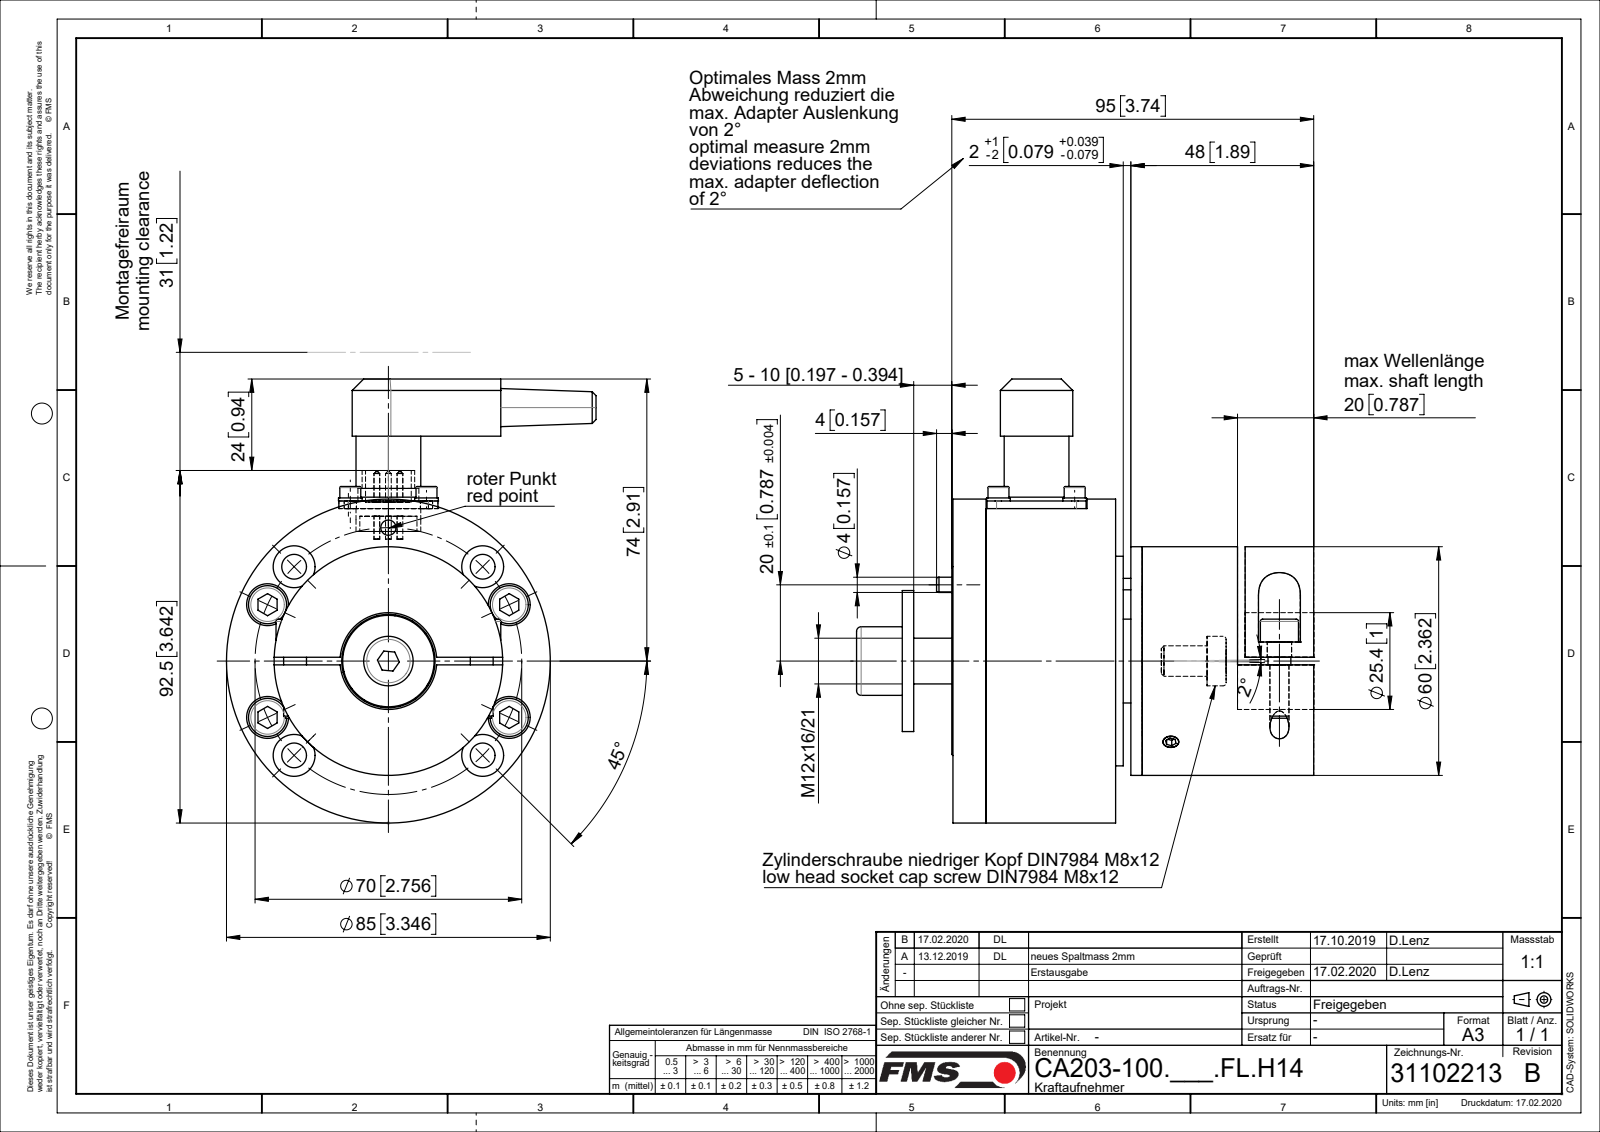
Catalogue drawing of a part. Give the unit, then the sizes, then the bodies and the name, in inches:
Units: inches
Overall size (bounding box): 4.744 × 4.587 × 3.819
Round holes (diameter × count): ⌀0.102 ×8, ⌀0.256 ×8, ⌀0.433 ×8, ⌀0.203 ×6, ⌀0.079 ×5, ⌀0.126 ×4, ⌀0.142 ×4, ⌀0.157 ×4, ⌀0.276 ×4, ⌀0.252 ×2, ⌀0.118 ×1, ⌀0.17 ×1
Round bosses / shafts (diameter × count): ⌀0.236 ×10, ⌀0.118 ×8, ⌀0.394 ×6, ⌀0.059 ×5, ⌀0.244 ×4, ⌀0.217 ×4, ⌀0.197 ×4, ⌀3.346 ×1
Partial cylindrical surfaces — rounded edges, fillets, slot ends (radius × count): R0.098 ×4, R0.197 ×2, R0.217 ×2, R0.374 ×1
Main face-to-face distances: 1.772, 1.949, 0.354, 0.079, 0.453, 1.24, 0.394, 1.693, 0.059, 1.594
Hole centre spacings: 0.787, 0.976, 0.992, 1.291, 1.378, 2.013, 2.223, 0.236
Volume: 19.74 in³ · Surface area: 174.5 in²
Bodies: 37 solids, 685 faces (229 planar, 315 cylindrical, 141 other)
Part name (STEP PRODUCT): C0705311_DI100; C0709081; C0612056; C0709072 (+8 more)
STEP written by: Mechanical Desktop 2009 (CONFIG_CONTROL_DESIGN)
